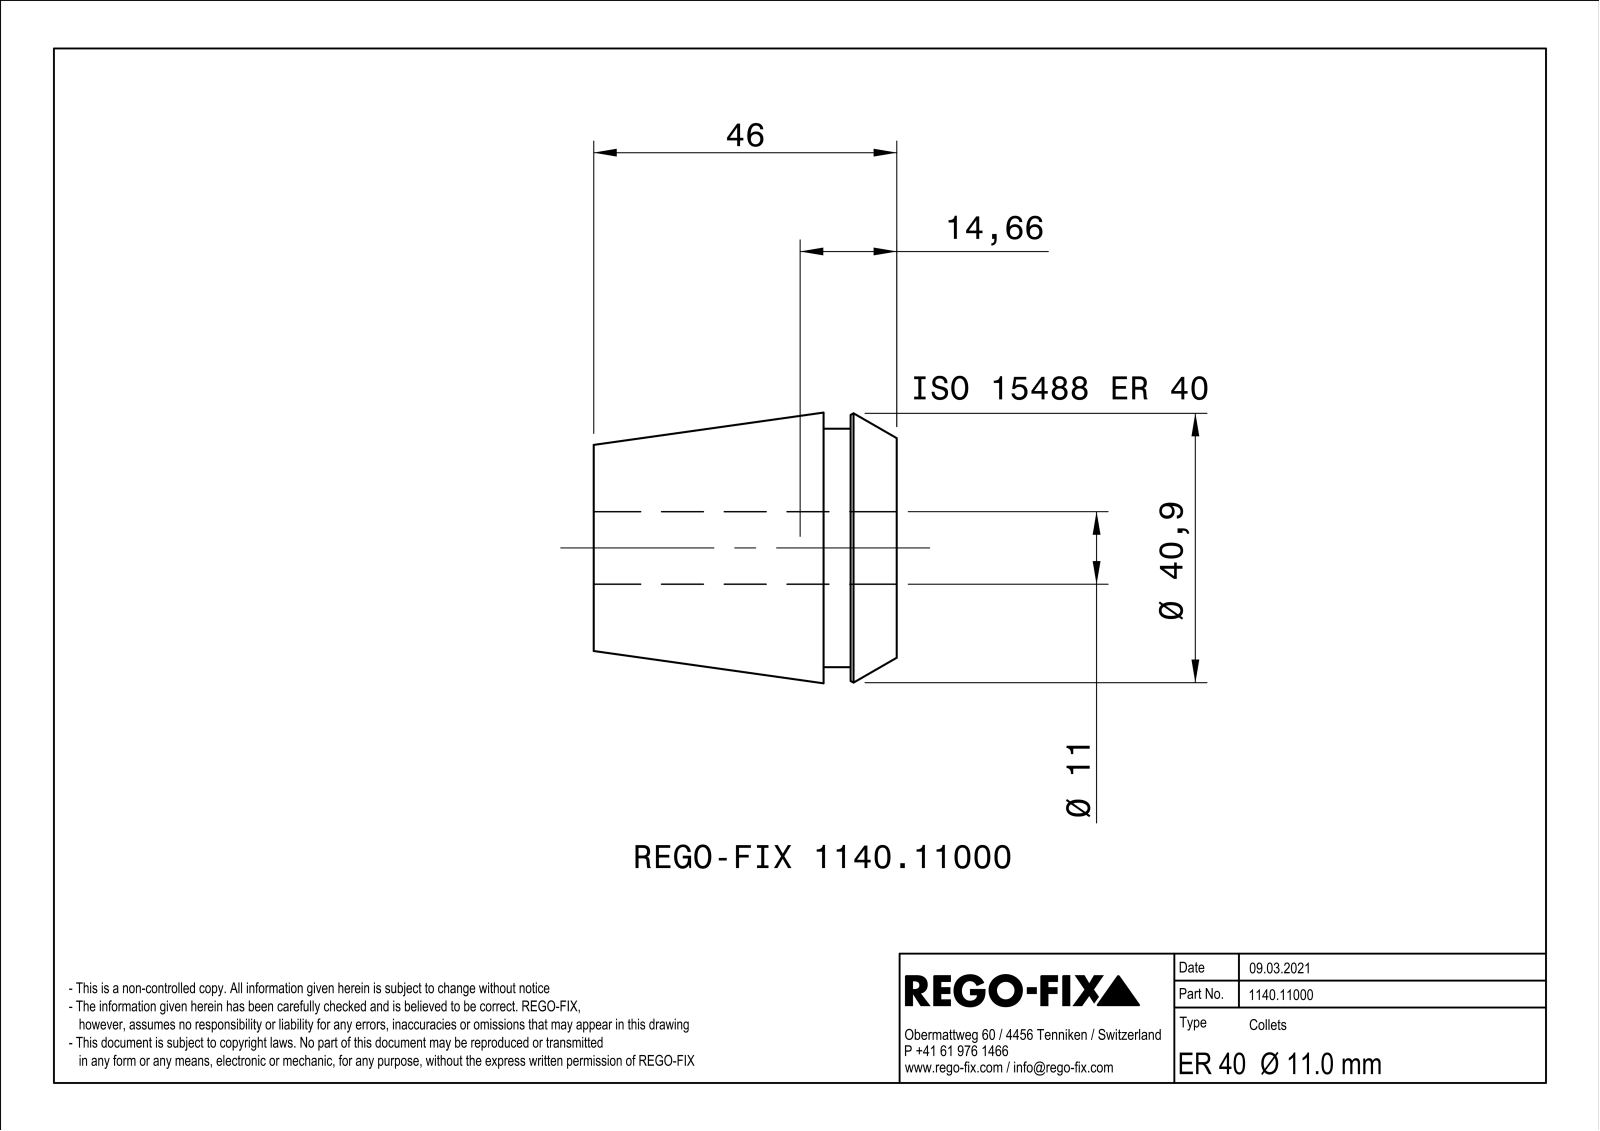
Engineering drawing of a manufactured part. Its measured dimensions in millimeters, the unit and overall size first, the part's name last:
Units: millimetres
Overall size (bounding box): 46 × 40.99 × 40.99
Round holes (diameter × count): ⌀11 ×1
Round bosses / shafts (diameter × count): ⌀36.2 ×1
Main face-to-face distances: 1, 46, 11.1, 34.9, 7, 4.1, 39, 7.5, 0.5, 3.6
Volume: 35 231 mm³ · Surface area: 24 075 mm²
Bodies: 1 solid, 177 faces (88 planar, 9 cylindrical, 80 other)
Part name (STEP PRODUCT): NOCUT
STEP written by: SIEMENS PLM Software Solid Edge ST10 (AUTOMOTIVE_DESIGN)
